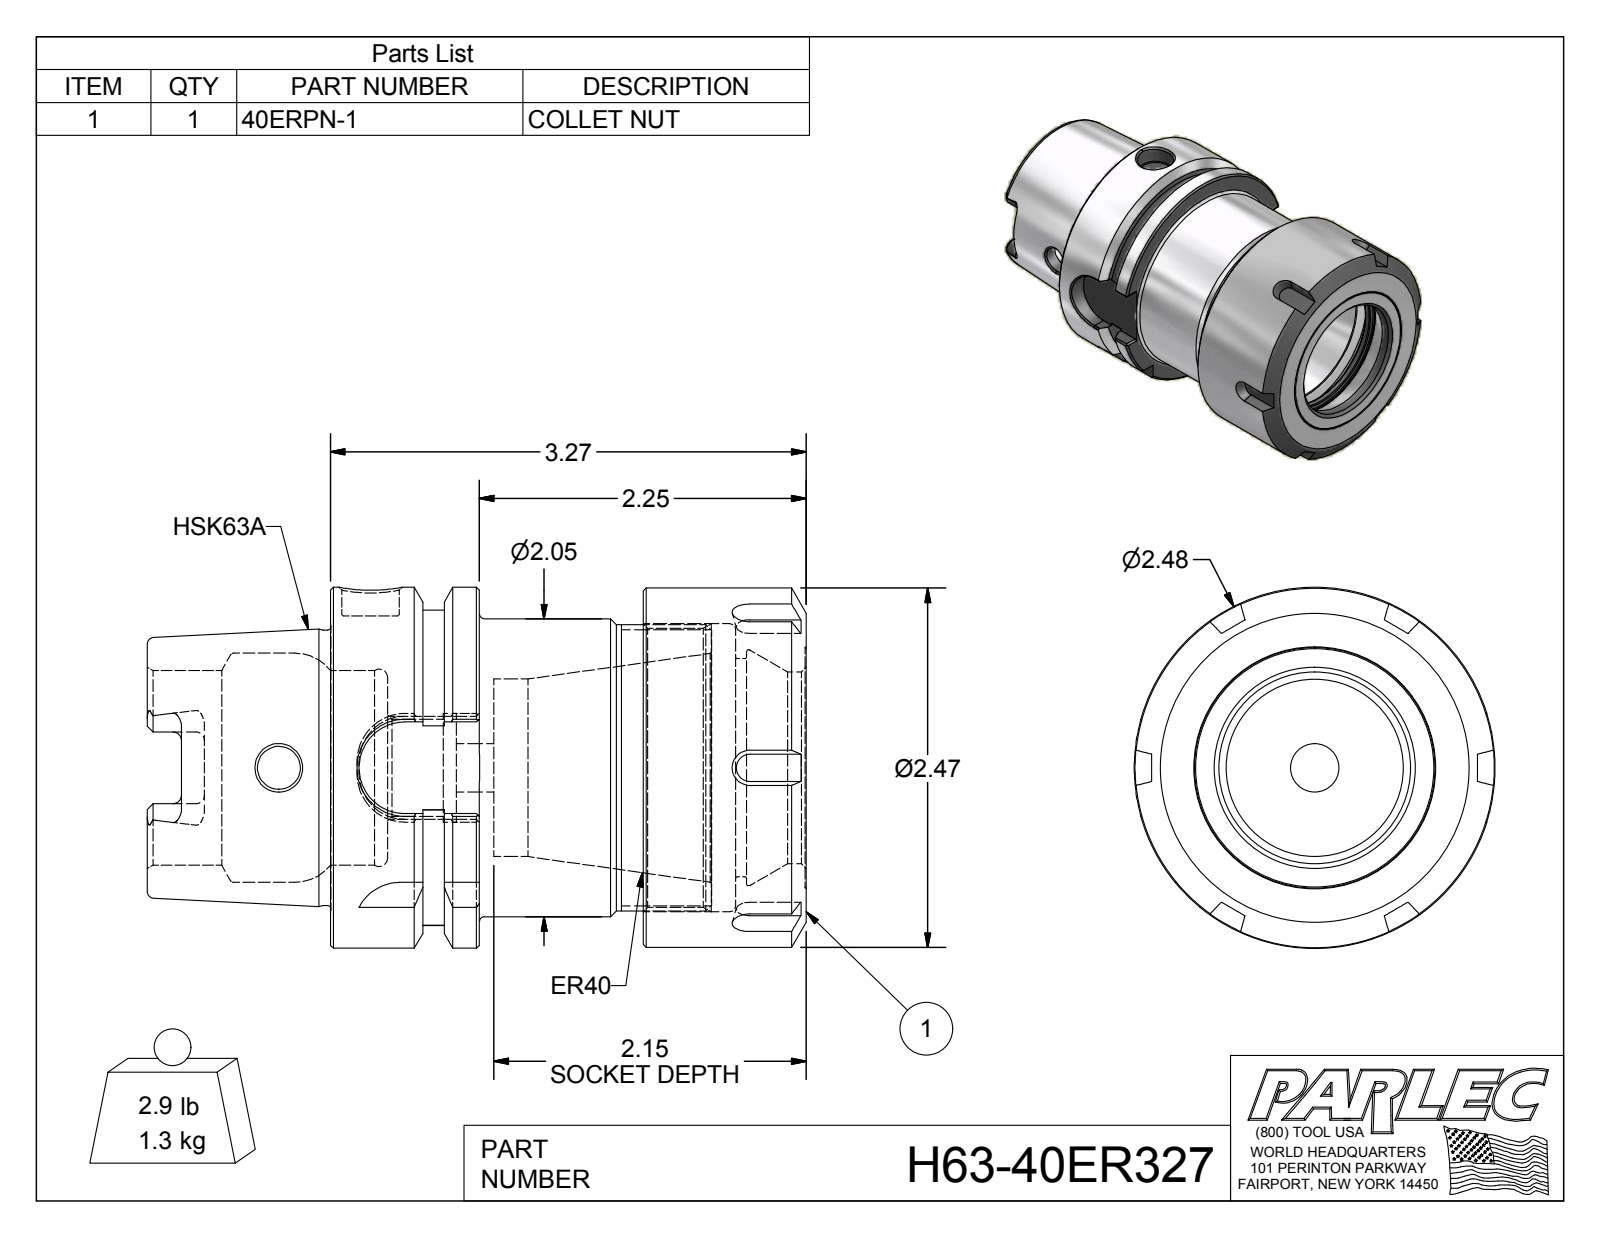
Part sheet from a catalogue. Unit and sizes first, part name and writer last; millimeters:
Units: millimetres
Overall size (bounding box): 115.1 × 63 × 63
Round holes (diameter × count): ⌀7.5 ×1, ⌀8.4 ×1, ⌀10 ×1, ⌀16.9 ×1, ⌀19 ×1, ⌀31 ×1, ⌀33.5 ×1, ⌀34 ×1, ⌀38.1 ×1, ⌀40 ×1, ⌀41.1 ×1, ⌀48.7 ×1
Round bosses / shafts (diameter × count): ⌀63 ×1, ⌀62.7 ×1, ⌀52 ×1, ⌀50 ×1, ⌀48 ×1
Partial cylindrical surfaces — rounded edges, fillets, slot ends (radius × count): R1.5 ×6, R2.9 ×4, R8 ×4, R27.5 ×1
Main face-to-face distances: 28.4, 54.6, 83.1, 28.5, 26.1, 54.5, 26, 70.8, 42.2, 16.2
Volume: 170 100 mm³ · Surface area: 46 260 mm²
Bodies: 2 solids, 190 faces (80 planar, 42 cylindrical, 68 other)
Part name (STEP PRODUCT): H63-40ER327; H63-40ER3-1; 40ERPN
STEP written by: Autodesk Inventor 2012 (AUTOMOTIVE_DESIGN)
